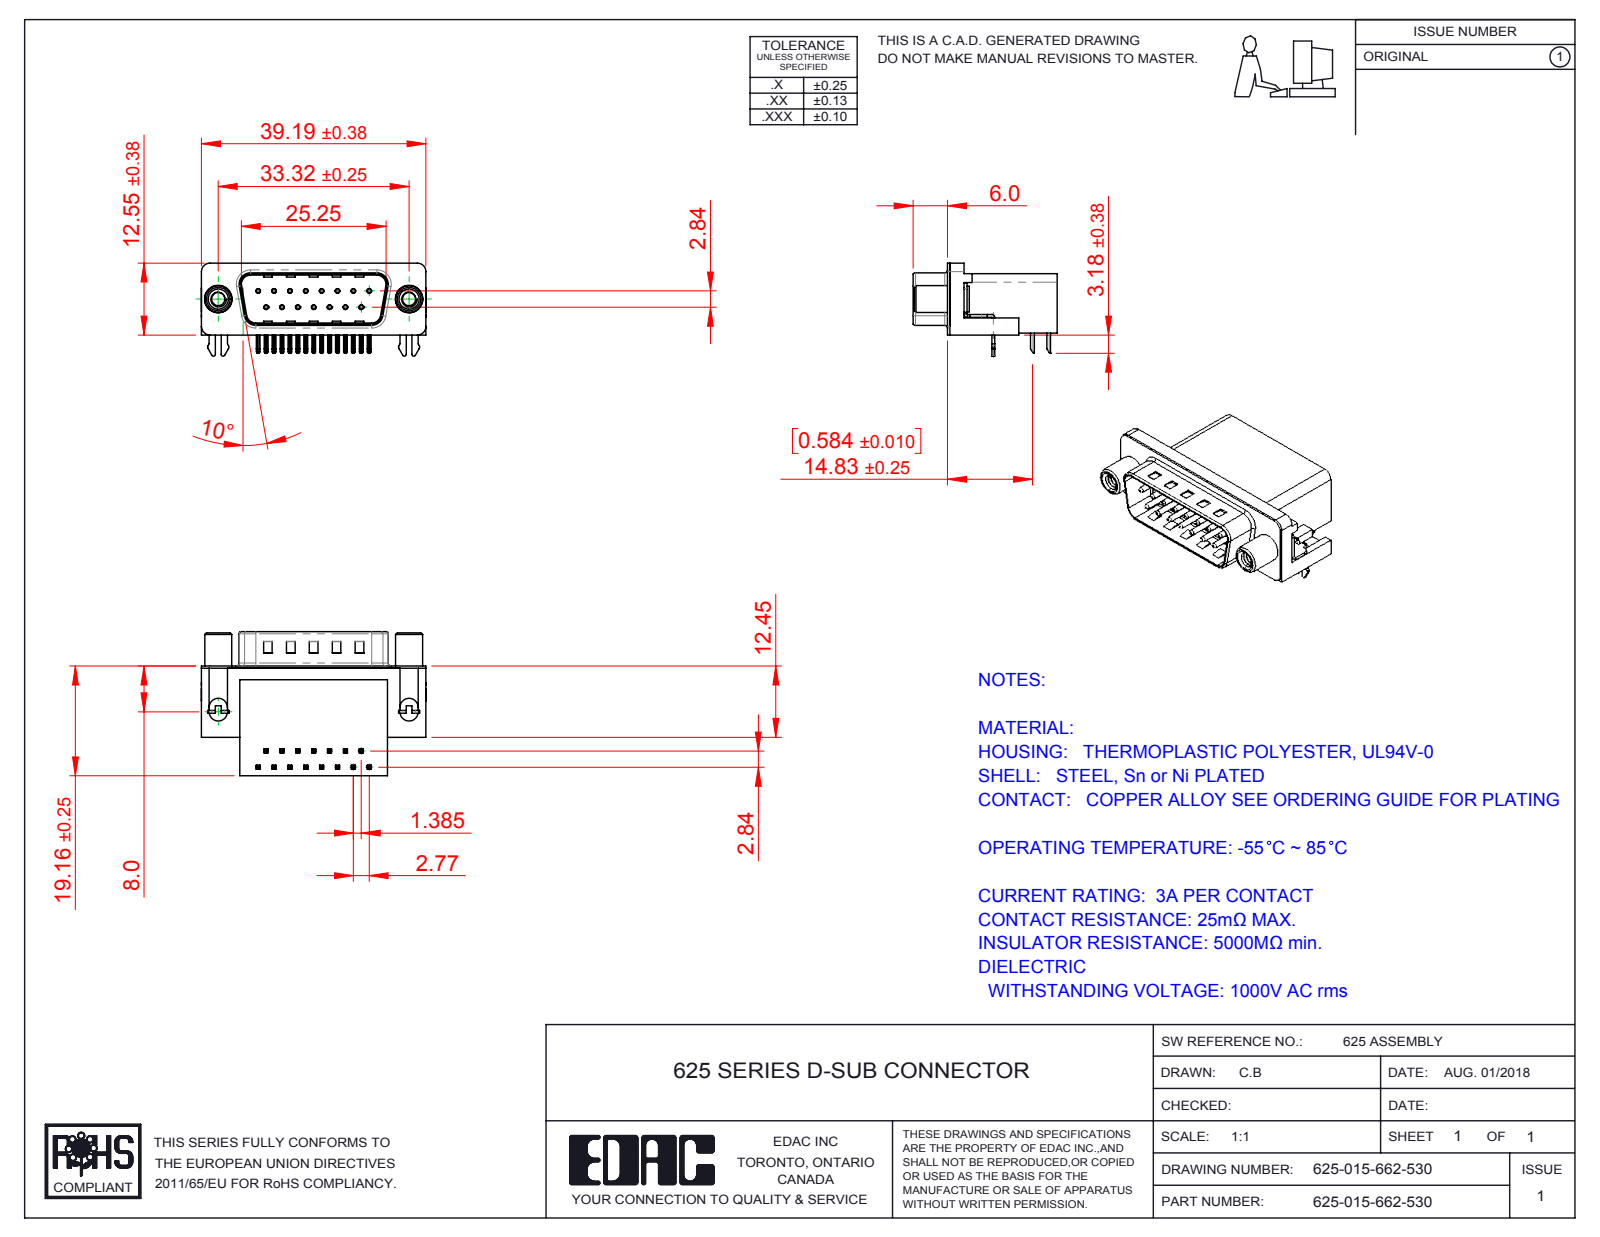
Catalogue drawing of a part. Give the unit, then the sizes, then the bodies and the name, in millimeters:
Units: millimetres
Overall size (bounding box): 39.22 × 25.16 × 16.25
Round holes (diameter × count): ⌀0.35 ×15, ⌀0.8 ×15, ⌀2.3 ×2, ⌀3.1 ×2, ⌀4 ×2, ⌀4.8 ×2, ⌀5 ×2
Round bosses / shafts (diameter × count): ⌀0.75 ×15, ⌀4.9 ×2, ⌀4.7 ×2, ⌀4.5 ×2, ⌀3.85 ×2
Partial cylindrical surfaces — rounded edges, fillets, slot ends (radius × count): R0.25 ×60, R0.12 ×30, R1 ×16, R0.5 ×14, R1.6 ×8, R1.5 ×6, R0.32 ×4, R0.9 ×4
Main face-to-face distances: 0.4, 10.35, 18.76, 2.1, 10.46, 1.7, 19.16, 10.86, 8.76, 16.26
Hole centre spacings: 3.16, 2.77, 5.54, 8.31, 11.08, 5.03, 5.04, 7.48
Volume: 6 332 mm³ · Surface area: 6 630 mm²
Bodies: 21 solids, 1513 faces (917 planar, 463 cylindrical, 133 other)
Part name (STEP PRODUCT): 625 Round Threaded Standoff; 625 Contact Top; 625 2 Prong Board Lock; 625 Contact Bottom (+3 more)
STEP written by: SolidWorks 2016 (CONFIG_CONTROL_DESIGN)
